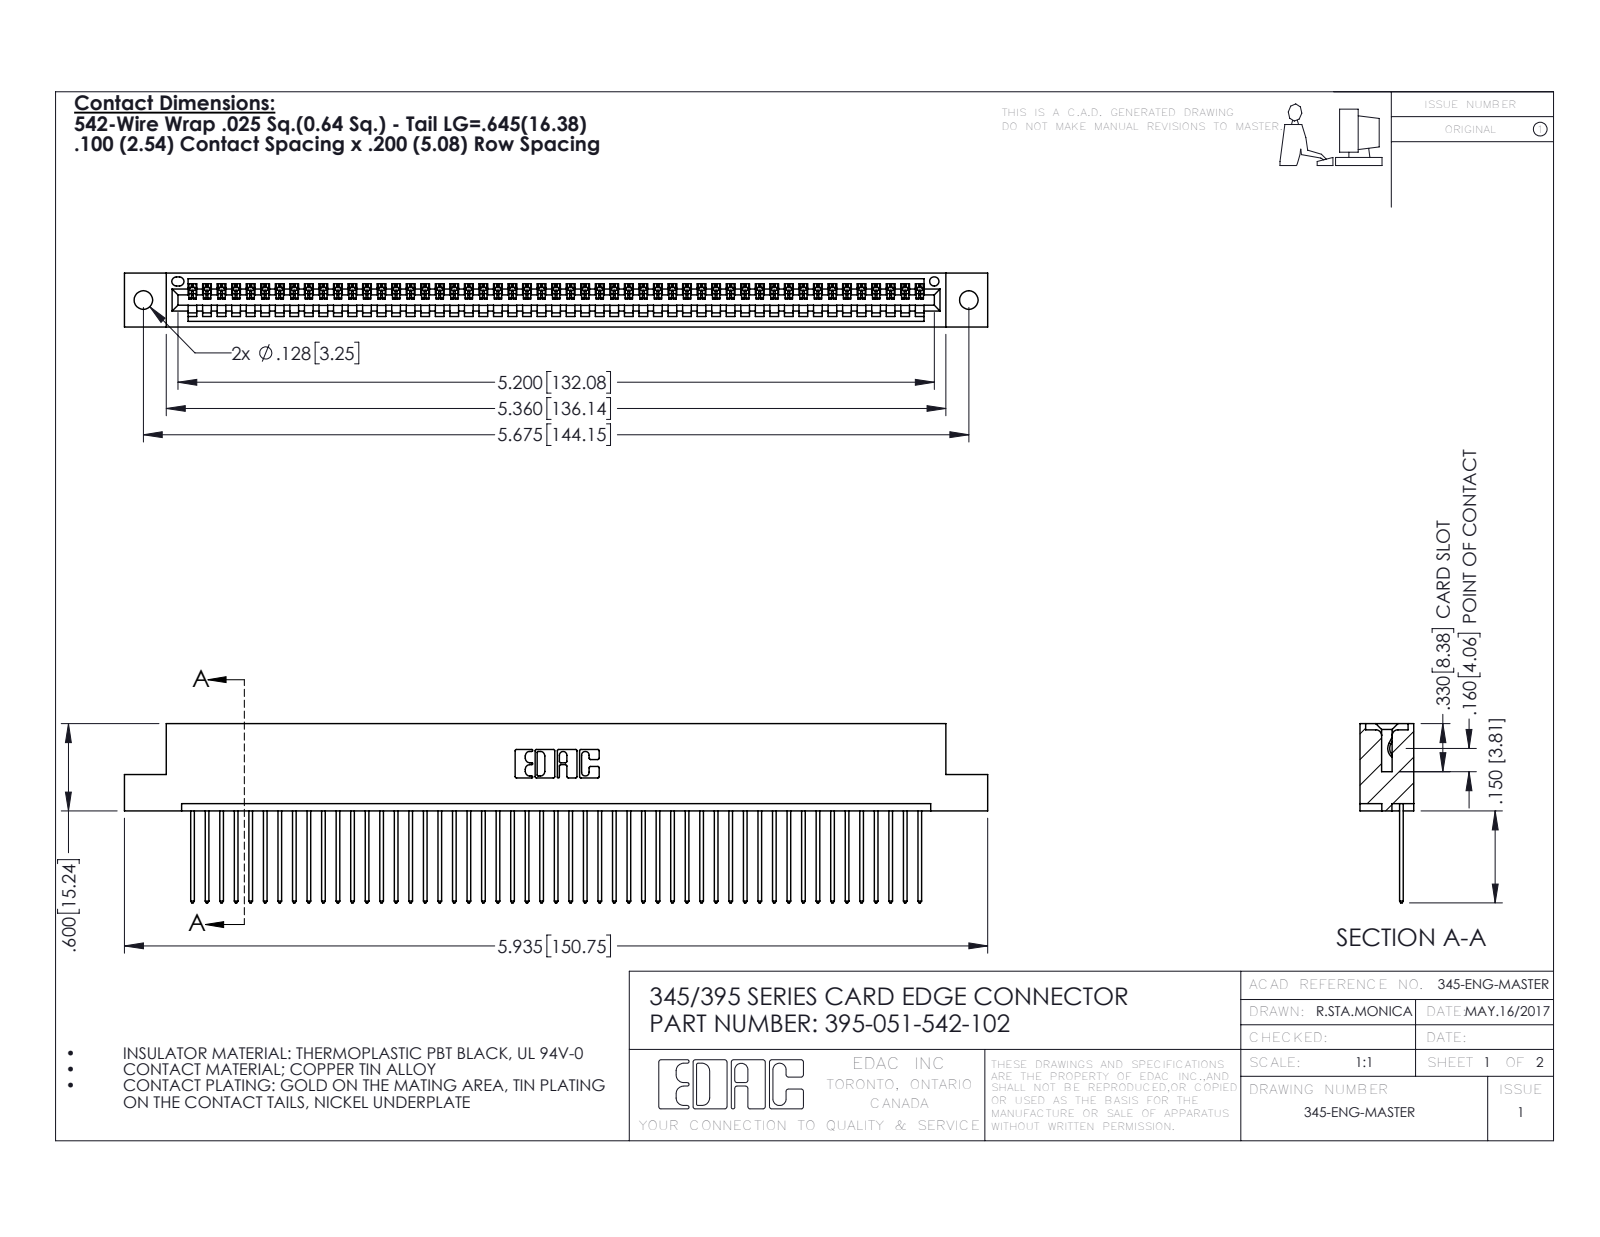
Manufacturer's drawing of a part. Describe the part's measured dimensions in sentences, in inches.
The part is named "395-051-542-102; 345-292-001_345-293-142; 345 Part_Flush Mounting Lugs - 0.128 Dia". Its 3-D file was written by "SolidWorks 2016 (CONFIG_CONTROL_DESIGN)". It is 52 solids with 3084 faces: 2120 planar, 964 cylindrical and 0 other. Overall it measures 5.935 by 1.232 by 0.37 inches. Its volume is 0.883 cubic inches and its surface area 30.68 square inches. Round holes: 2 of diameter 0.128, 1 of diameter 0.064. Partial cylindrical surfaces (rounded edges, fillets, slot ends): 102 of radius 0.006, 102 of radius 0.01, 22 of radius 0.01, 6 of radius 0.007, 6 of radius 0.031, 3 of radius 0.026, 2 of radius 0.031, 2 of radius 0.04. The main face-to-face distances are 0.072, 0.298, 0.098, 0.272, 0.025, 0.37, 0.2, 0.225, 0.149, 0.072. The hole center spacings are 0.27, 5.439, 5.675.
